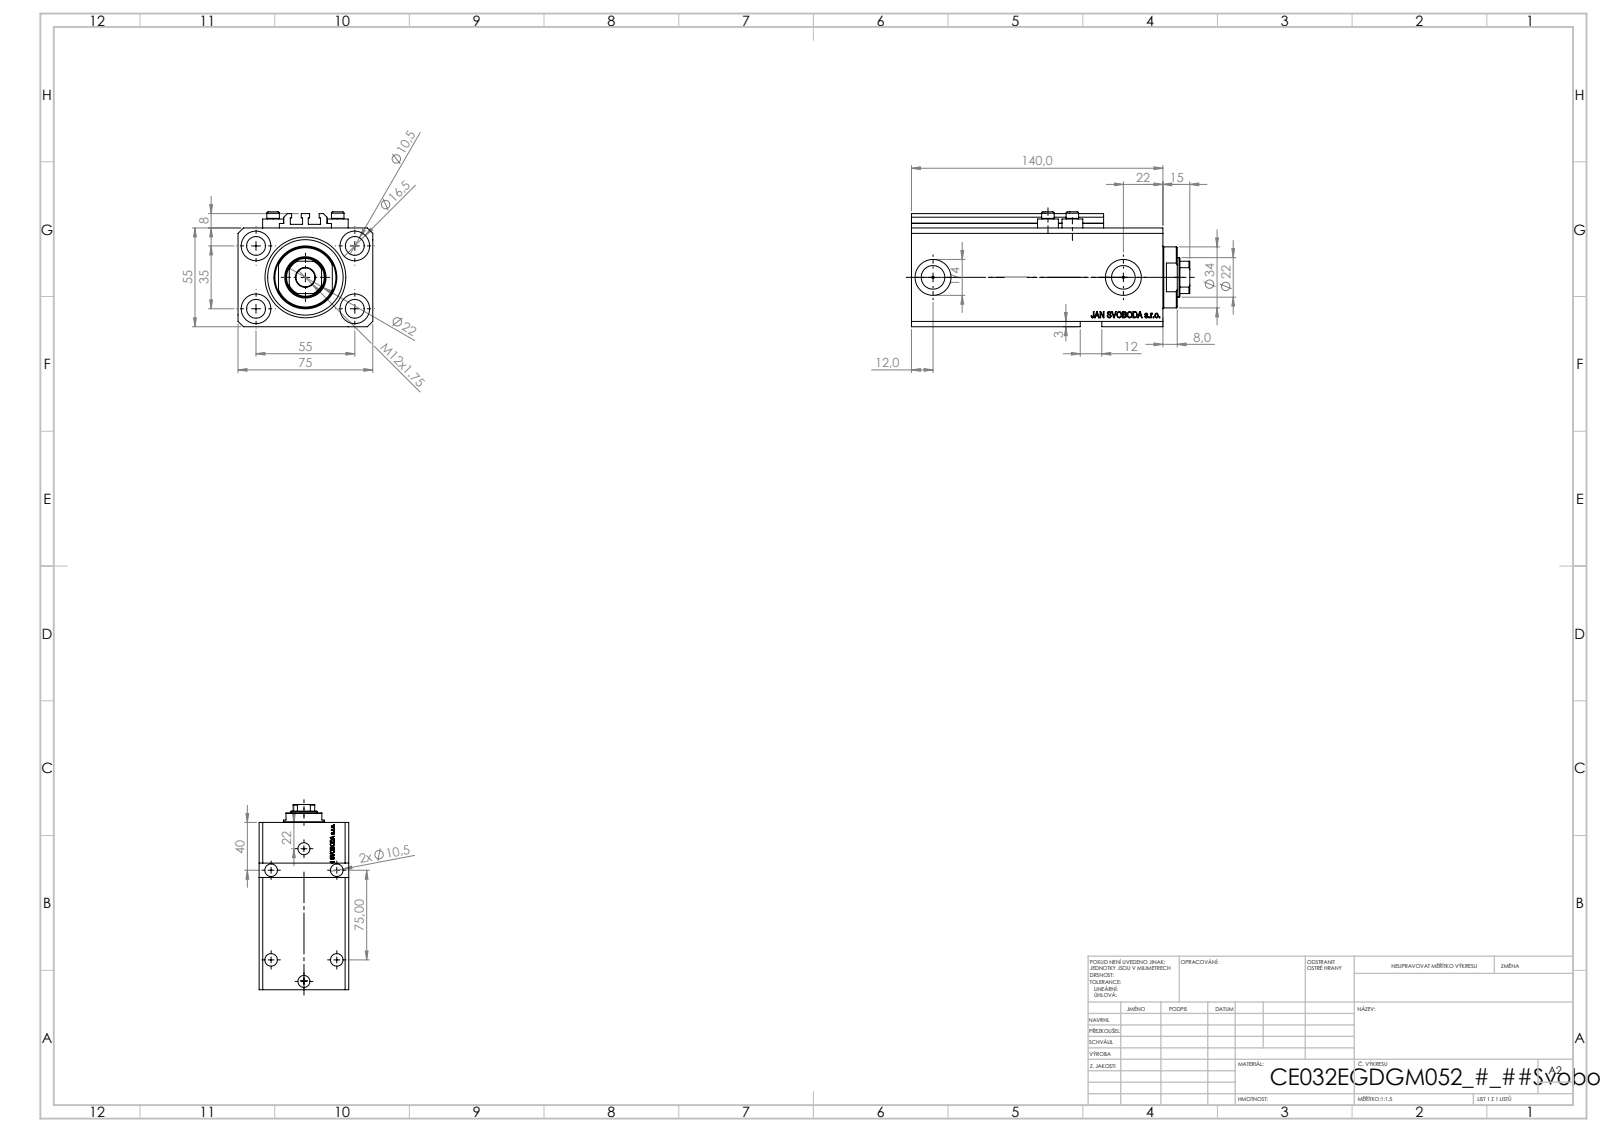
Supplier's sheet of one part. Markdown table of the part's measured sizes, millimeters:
| quantity | value |
| --- | --- |
| part name | V250CE_E_Body; V250CE_VC_E; ALLEN BOLT V250CE; V250CE_C_VCP |
| STEP written by | SolidWorks 2019 (CONFIG_CONTROL_DESIGN) |
| units | millimeters |
| bodies | 8 solids, 1100 faces (518 planar, 158 cylindrical, 424 other) |
| overall size | 155 × 75 × 64 |
| volume | 481 599 mm³ |
| surface area | 116 451 mm² |
| round holes (diameter × count) | 10.5 × 9, 1.25 × 4, 4 × 4, 16.5 × 4, 10 × 2, 13.16 × 2, 20 × 2, 22 × 1, 32 × 1, 45 × 1 |
| round bosses / shafts (diameter × count) | 11.6 × 4, 7 × 4, 34 × 1 |
| partial cylindrical surfaces (radius × count) | 0.2 × 10, 10.5 × 1 |
| main face-to-face distances | 55, 75, 15, 9.9, 140, 125, 3, 57, 115.1, 130.1 |
| hole center spacings | 32.6, 32.87, 55, 96.98, 13.6, 14.09, 25.81, 32.58 |
